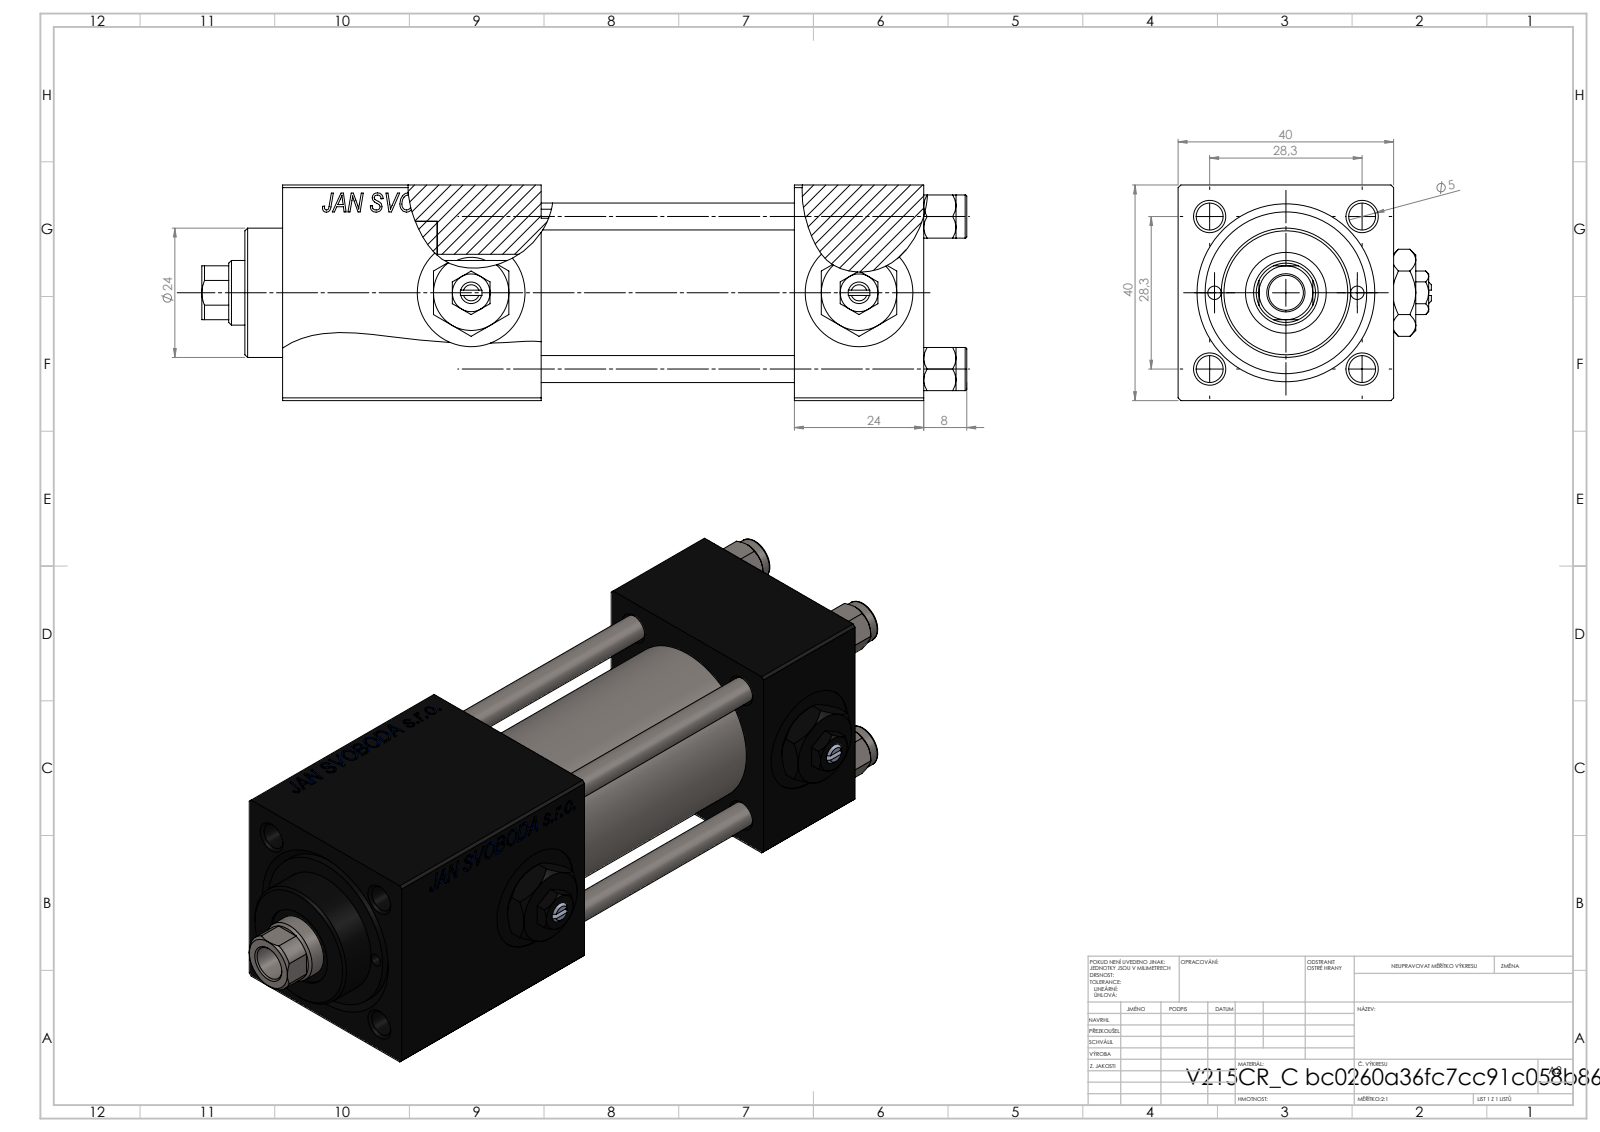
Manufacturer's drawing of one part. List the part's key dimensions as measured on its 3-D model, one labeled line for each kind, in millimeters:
Part name (STEP PRODUCT): V215CR_VCP_C; V215_VC_A; V215CR_C_TYCINKA; Zatka_pro_OIL_PORT (+2 more)
STEP written by: SolidWorks 2019 (CONFIG_CONTROL_DESIGN)
Units: millimetres
Bodies: 13 solids, 1254 faces (574 planar, 102 cylindrical, 578 other)
Overall size (bounding box): 142 × 47 × 40
Volume: 140 936 mm³ · Surface area: 56 288 mm²
Round holes (diameter × count): ⌀5 ×4, ⌀20 ×3, ⌀2.5 ×2, ⌀7 ×2, ⌀13.16 ×2, ⌀6.5 ×1, ⌀12 ×1, ⌀15 ×1, ⌀25 ×1, ⌀30 ×1
Round bosses / shafts (diameter × count): ⌀8 ×4, ⌀31 ×1, ⌀24 ×1
Partial cylindrical surfaces — rounded edges, fillets, slot ends (radius × count): R5.5 ×1
Main face-to-face distances: 40, 24, 39.8, 90.3, 66.3, 47, 48, 71, 19.3, 95
Hole centre spacings: 14.18, 20.01, 28.3, 30.84, 13.25, 40.02, 26.5, 72
